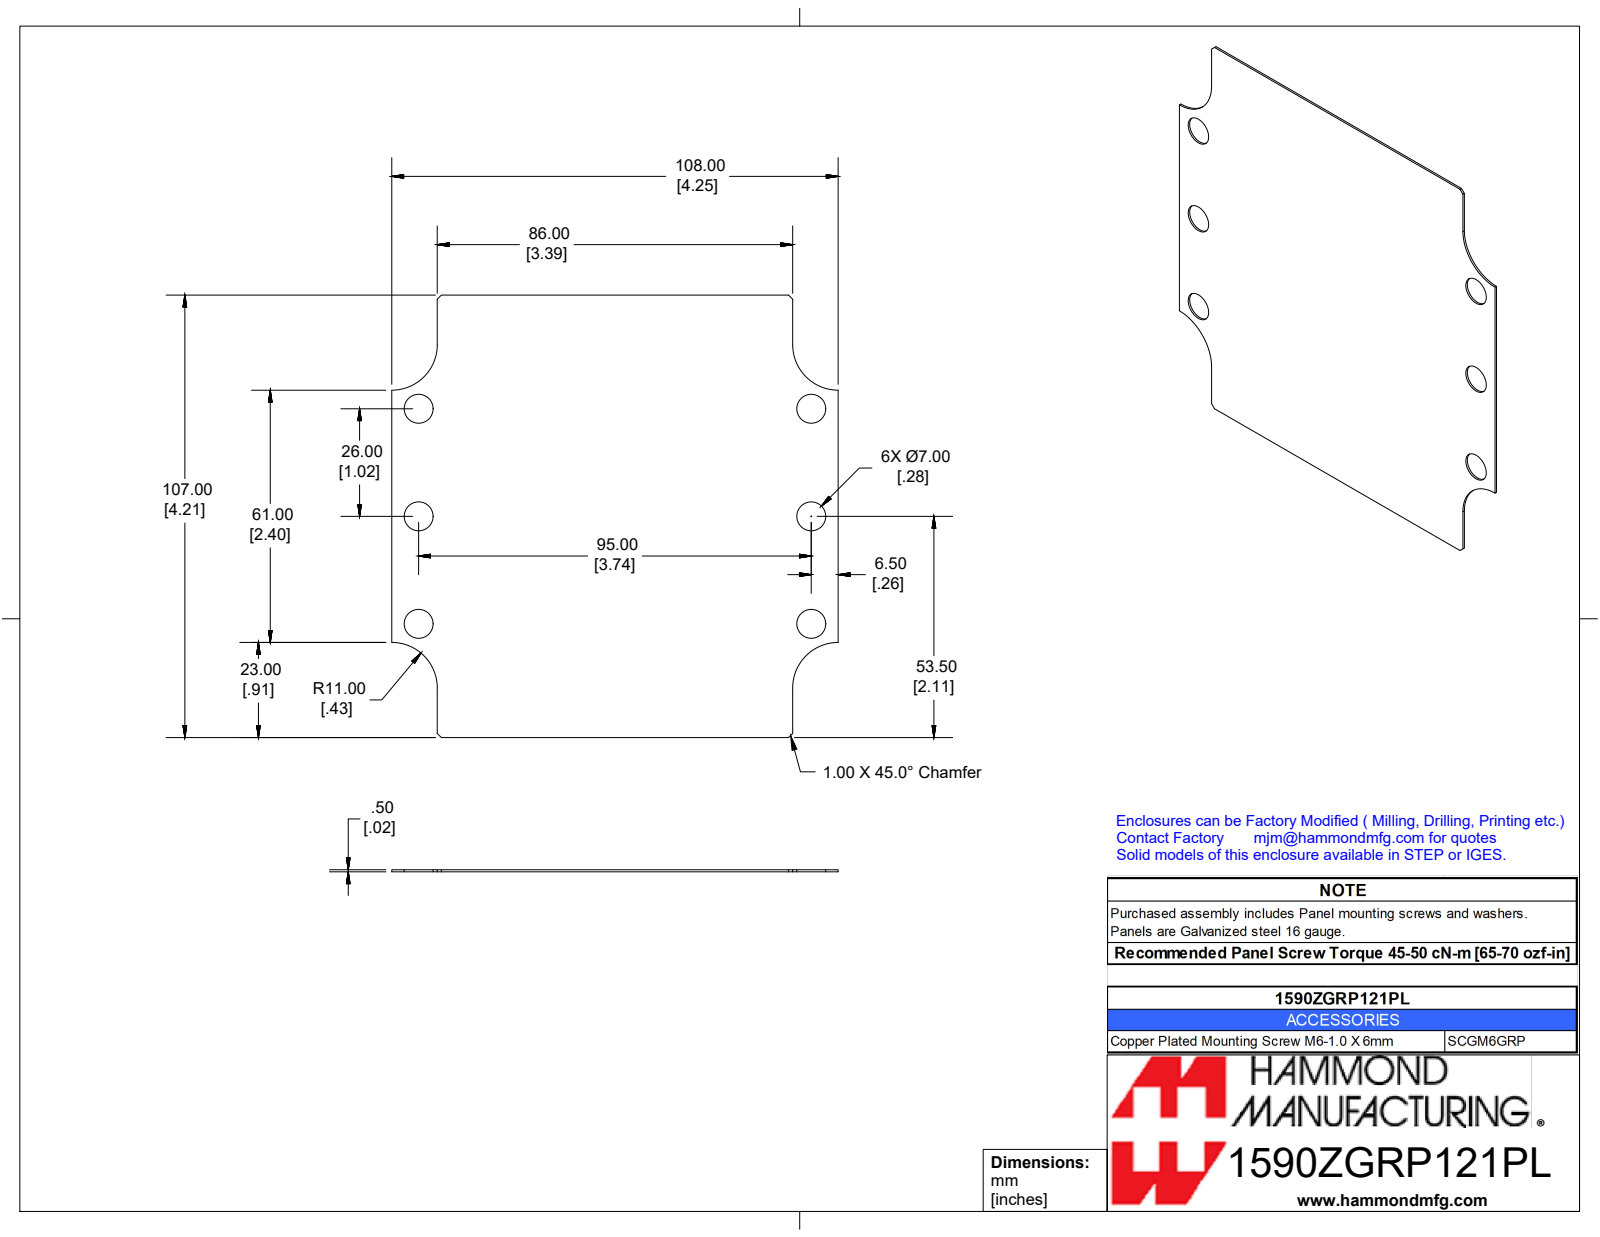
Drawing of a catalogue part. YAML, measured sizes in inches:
part_name: "1590ZGRP121PL"
step_written_by: "SolidWorks 2019 (CONFIG_CONTROL_DESIGN)"
units: inches
bodies: {solids: 1, faces: 24, planar: 14, cylindrical: 10, other: 0}
overall_size: [4.252, 4.213, 0.02]
volume: 0.318
surface_area: 32.71
round_holes:
  - {diameter: 0.276, count: 6}
partial_cylinders:
  - {radius: 0.433, count: 4}
face_to_face_distances: [0.02, 4.213, 4.252, 0.433, 3.819, 3.386, 5.317]
hole_center_spacings: [1.024, 3.878, 3.74, 2.047, 4.264]
